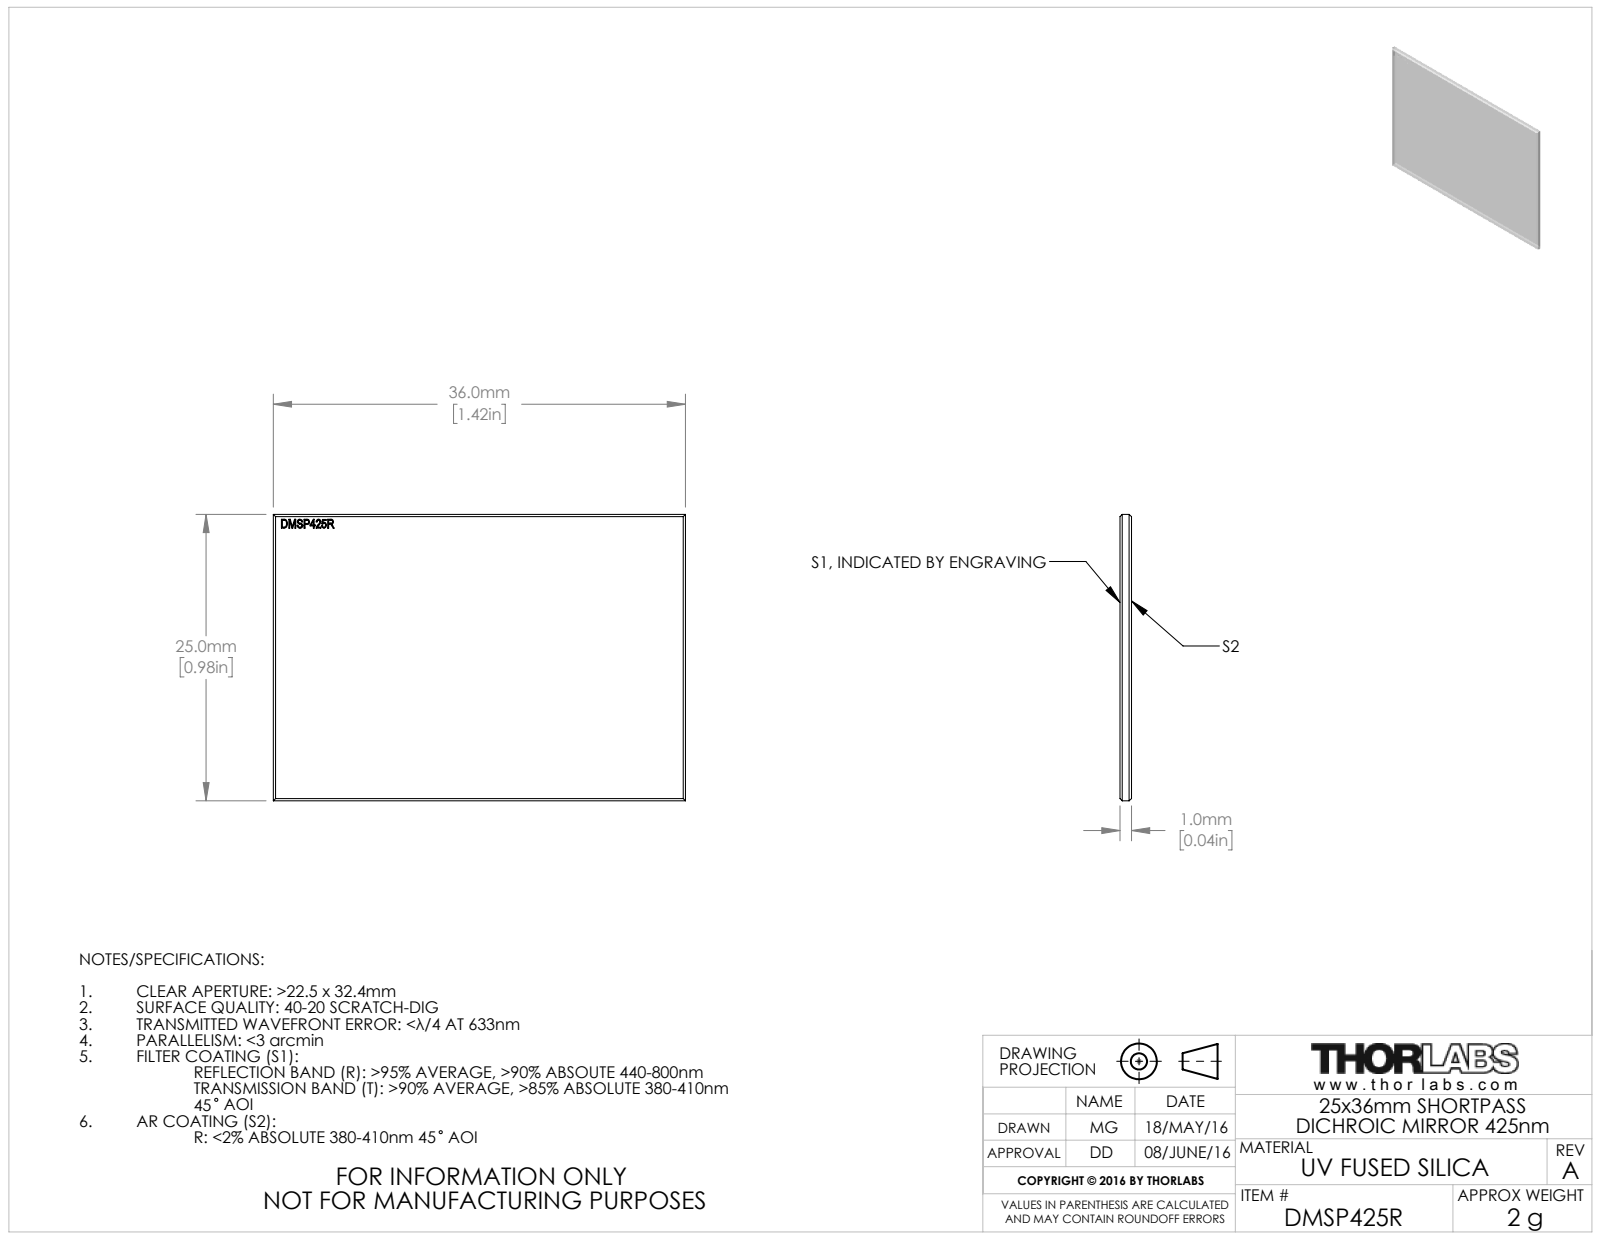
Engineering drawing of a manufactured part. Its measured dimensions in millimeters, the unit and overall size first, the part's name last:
Units: millimetres
Overall size (bounding box): 36 × 25 × 1
Main face-to-face distances: 1, 25, 18.1, 36, 25.88, 0.99, 0.8, 0.72, 1.97, 2.77
Volume: 895 mm³ · Surface area: 1 894 mm²
Bodies: 1 solid, 142 faces (92 planar, 0 cylindrical, 50 other)
Part name (STEP PRODUCT): TTN045175-E0W
STEP written by: SolidWorks 2016 (CONFIG_CONTROL_DESIGN)
